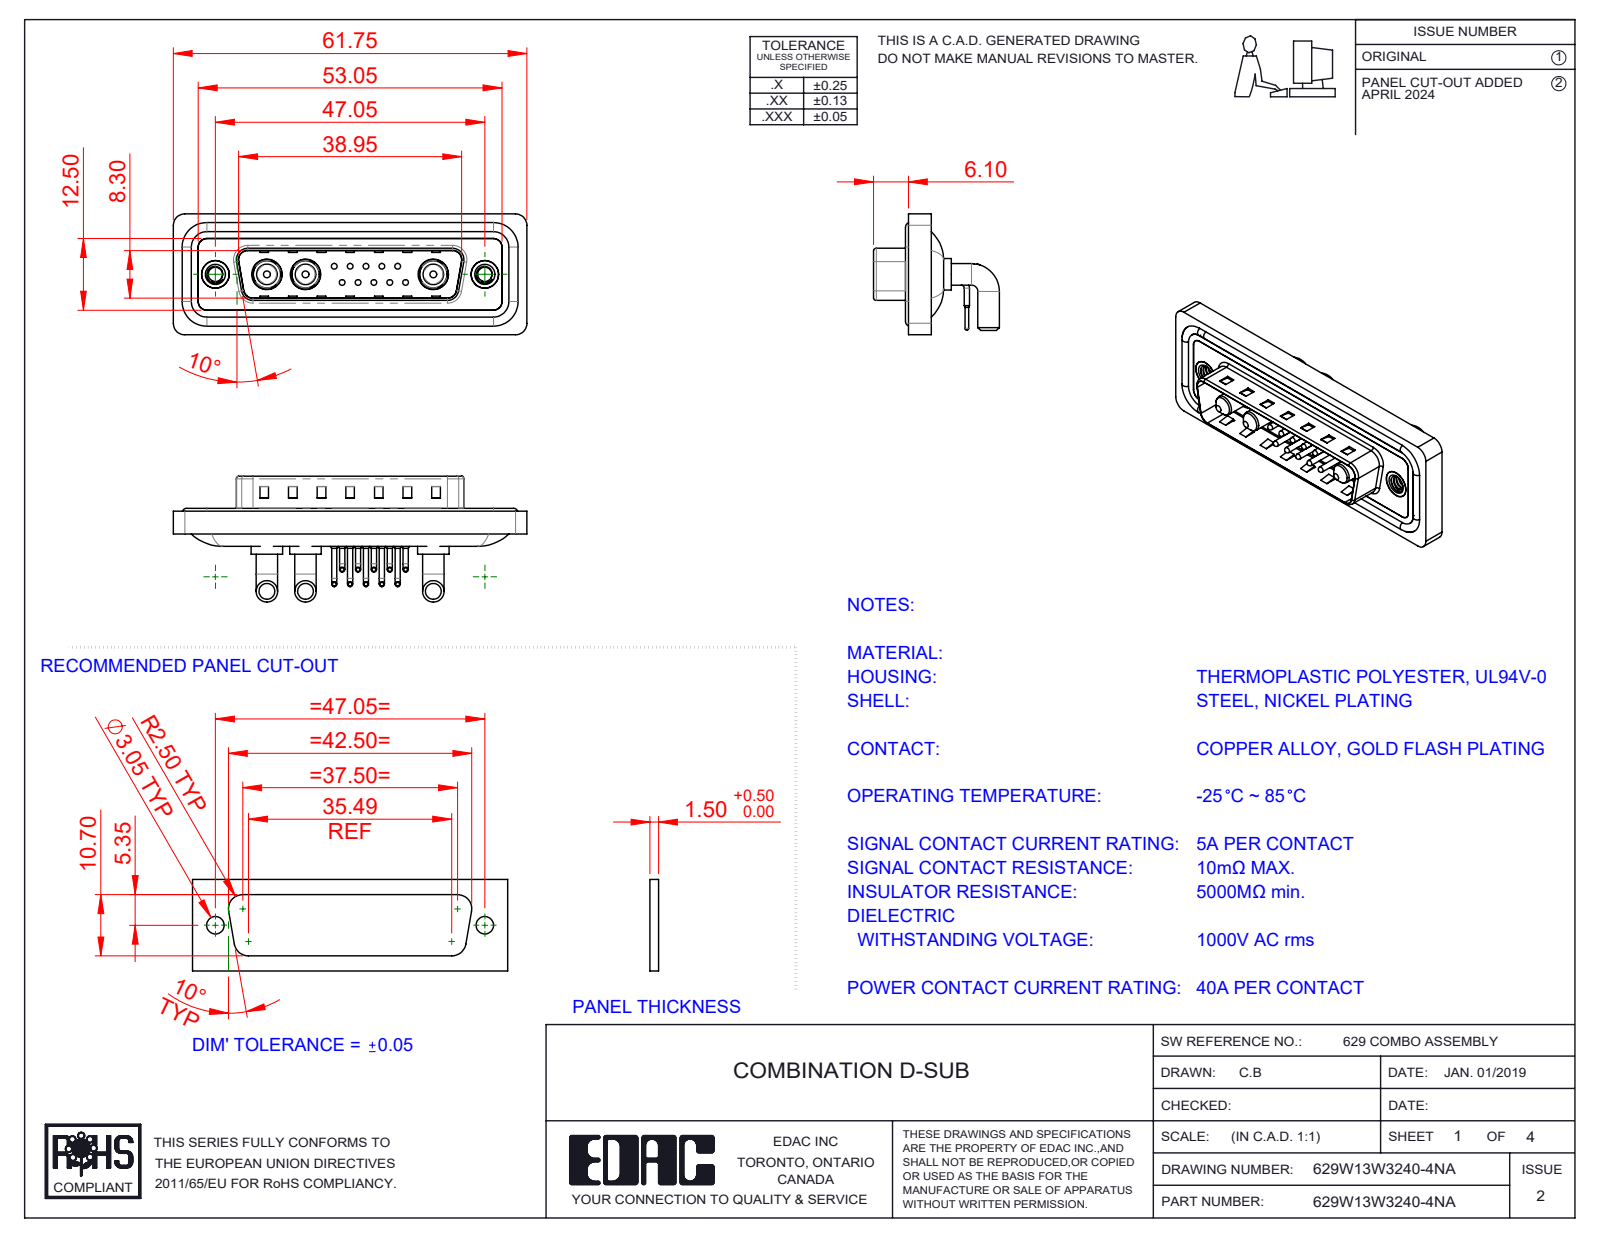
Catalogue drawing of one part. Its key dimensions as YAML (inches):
part_name: "629Combo Shell Front_25 Contacts; 629Combo Contact Row 1; 629Combo Waterproof Housing_25 Contacts; 629Combo Housing_13W3 (+5 more)"
step_written_by: "SolidWorks 2023 (CONFIG_CONTROL_DESIGN)"
units: inches
bodies: {solids: 23, faces: 1706, planar: 879, cylindrical: 609, other: 218}
overall_size: [2.431, 0.865, 0.831]
volume: 0.478
surface_area: 19.58
round_holes:
  - {diameter: 0.03, count: 10}
  - {diameter: 0.063, count: 10}
  - {diameter: 0.079, count: 10}
  - {diameter: 0.191, count: 3}
  - {diameter: 0.209, count: 3}
  - {diameter: 0.098, count: 2}
  - {diameter: 0.157, count: 2}
  - {diameter: 0.189, count: 2}
  - {diameter: 0.197, count: 2}
round_bosses_or_shafts:
  - {diameter: 0.035, count: 20}
  - {diameter: 0.059, count: 10}
  - {diameter: 0.039, count: 10}
  - {diameter: 0.026, count: 10}
  - {diameter: 0.148, count: 6}
  - {diameter: 0.063, count: 4}
  - {diameter: 0.217, count: 3}
  - {diameter: 0.205, count: 3}
partial_cylinders:
  - {radius: 0.059, count: 18}
  - {radius: 0.079, count: 18}
  - {radius: 0.04, count: 10}
  - {radius: 0.02, count: 8}
  - {radius: 0.063, count: 8}
  - {radius: 0.01, count: 4}
  - {radius: 0.024, count: 4}
  - {radius: 0.026, count: 4}
face_to_face_distances: [0.016, 0.114, 0.031, 0.161, 0.043, 0.083, 0.063, 0.177, 0.059, 0.236]
hole_center_spacings: [0.124, 0.109, 0.198, 0.218, 0.295, 0.198, 0.327, 0.398]
